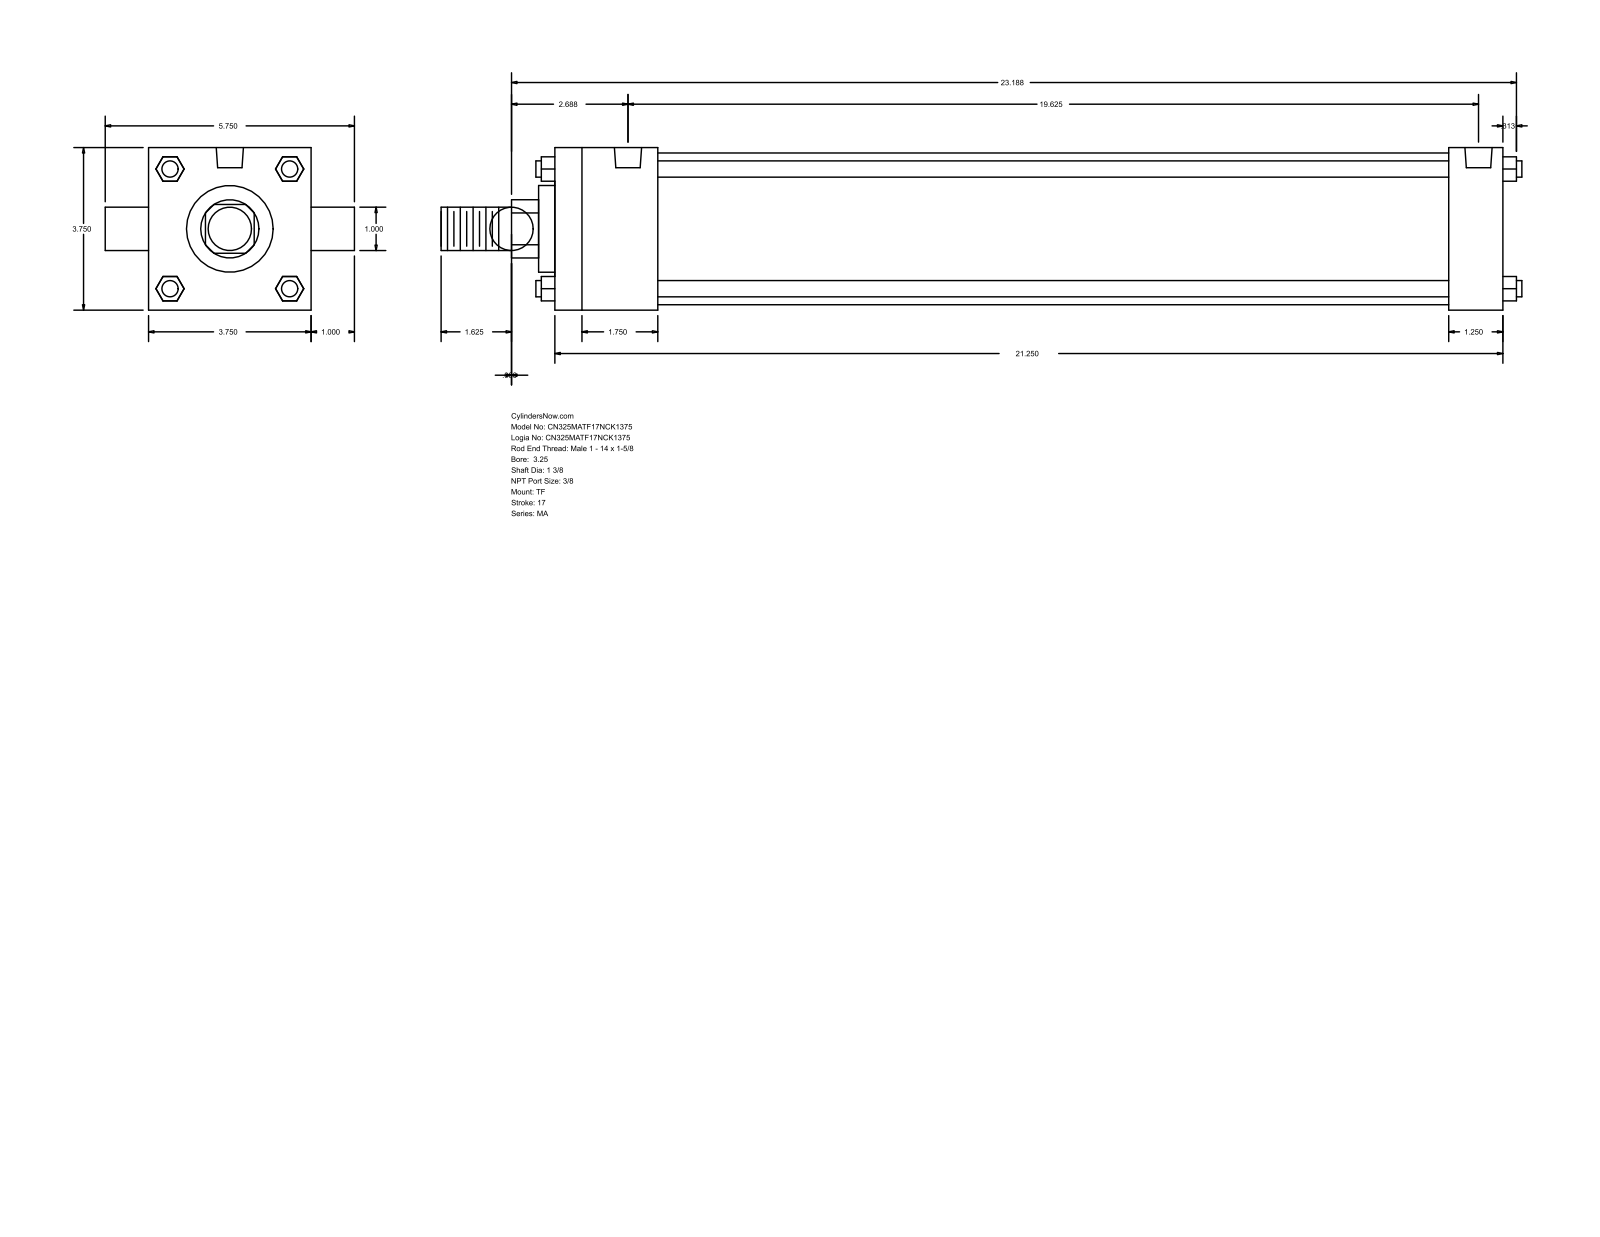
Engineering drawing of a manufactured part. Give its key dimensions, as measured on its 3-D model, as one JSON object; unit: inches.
{"part_name": "MA_TF__0325_1.375", "step_written_by": "GSSL Pune (CONFIG_CONTROL_DESIGN)", "units": "inches", "bodies": {"solids": 0, "faces": 120, "planar": 92, "cylindrical": 28, "other": 0}, "overall_size": [24.937, 5.75, 3.75], "round_holes": [[0.437, 3], [0.627, 2]], "round_bosses_or_shafts": [[0.375, 4], [1, 2], [3.5, 1], [2, 1], [1.375, 1]], "partial_cylinders_radius": [[0.672, 1]], "face_to_face_distances": [3.75, 21.875, 2.375, 20.625, 18.25, 19.5, 1.25, 0.375, 2.75, 21], "hole_center_spacings": [0.187, 0.188, 19.25, 19.437, 19.438, 19.625]}
